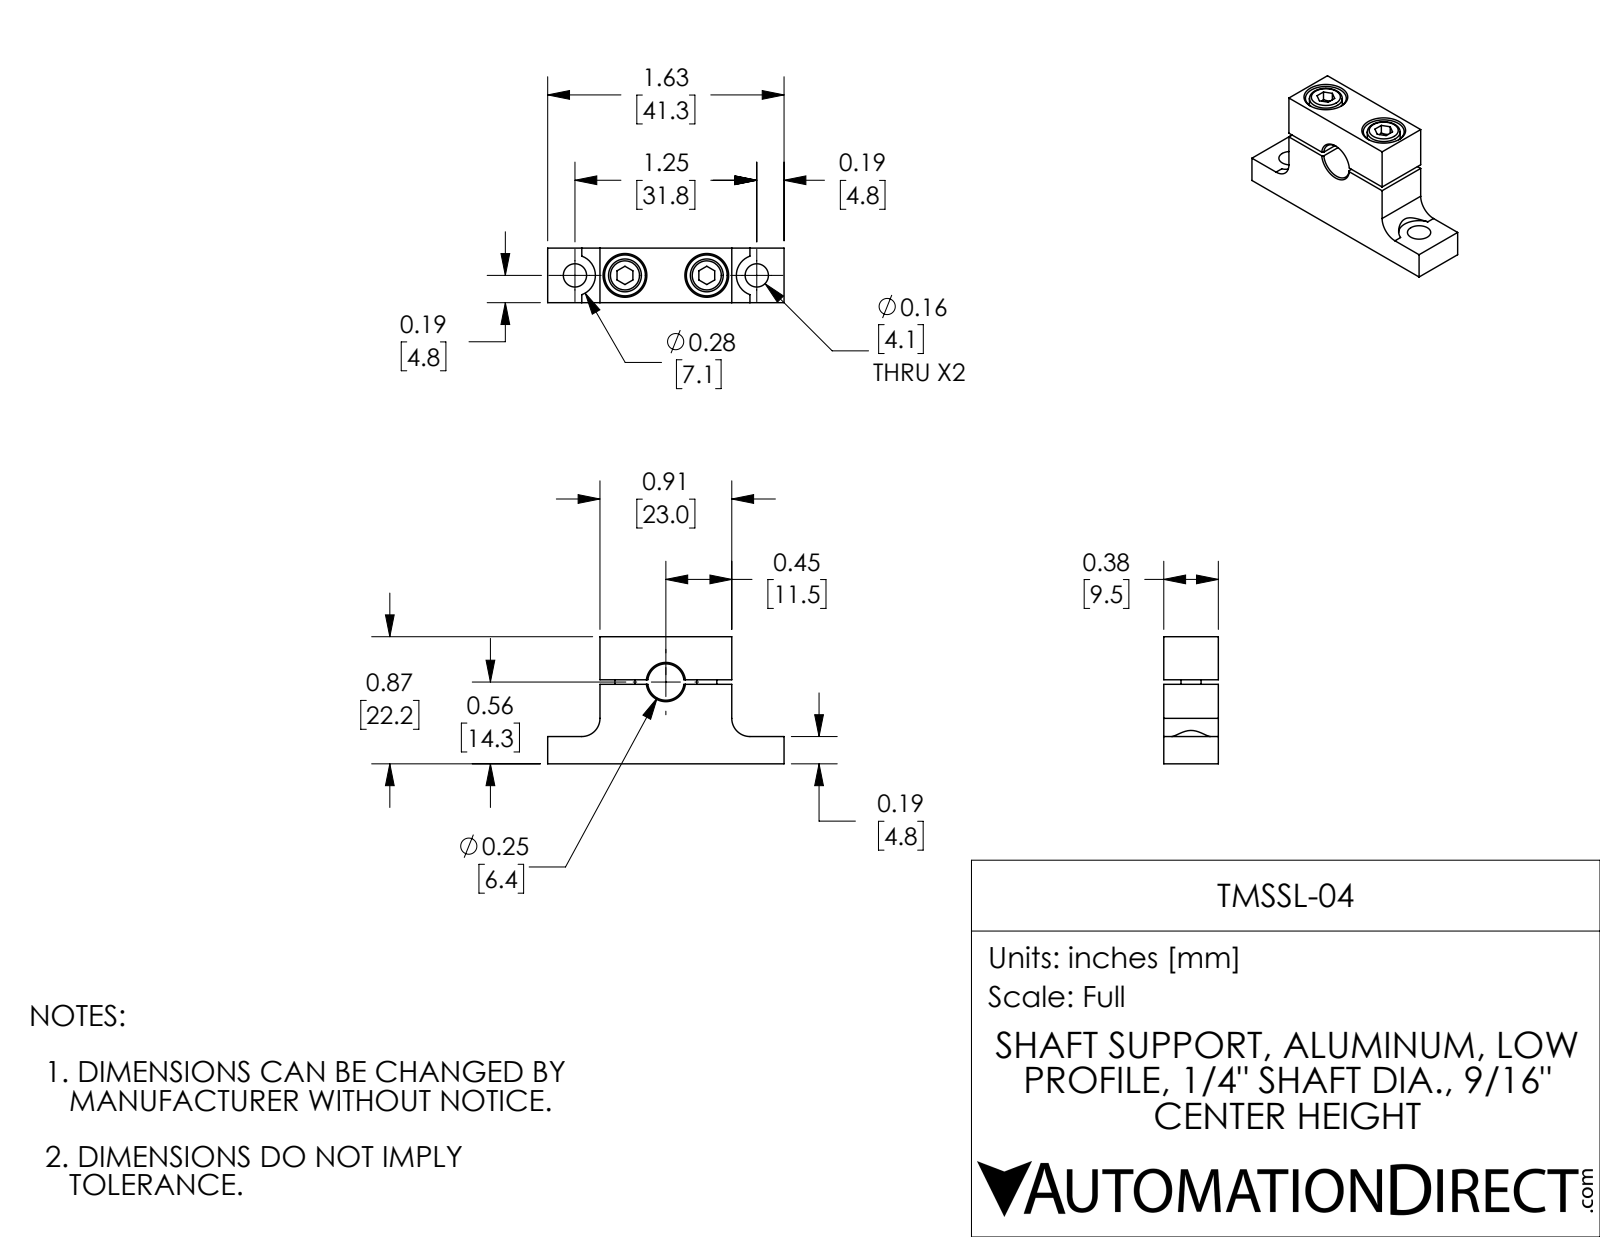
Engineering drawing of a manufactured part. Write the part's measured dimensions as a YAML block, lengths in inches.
part_name: "TMSSL-04"
step_written_by: "SolidWorks 2017 (AUTOMOTIVE_DESIGN)"
units: inches
bodies: {solids: 4, faces: 93, planar: 38, cylindrical: 31, other: 24}
overall_size: [1.625, 0.874, 0.375]
volume: 0.306
surface_area: 5.816
round_holes:
  - {diameter: 0.104, count: 2}
  - {diameter: 0.15, count: 2}
  - {diameter: 0.16, count: 2}
  - {diameter: 0.281, count: 2}
  - {diameter: 0.25, count: 1}
round_bosses_or_shafts:
  - {diameter: 0.226, count: 2}
  - {diameter: 0.138, count: 2}
partial_cylinders:
  - {radius: 0.125, count: 2}
  - {radius: 0.141, count: 2}
face_to_face_distances: [0.375, 0.873, 0.546, 0.327, 0.578, 0.031, 0.296, 0.906, 0.187, 0.359]
hole_center_spacings: [0.344, 0.344, 0.562, 0.906, 0.906, 1.25]
